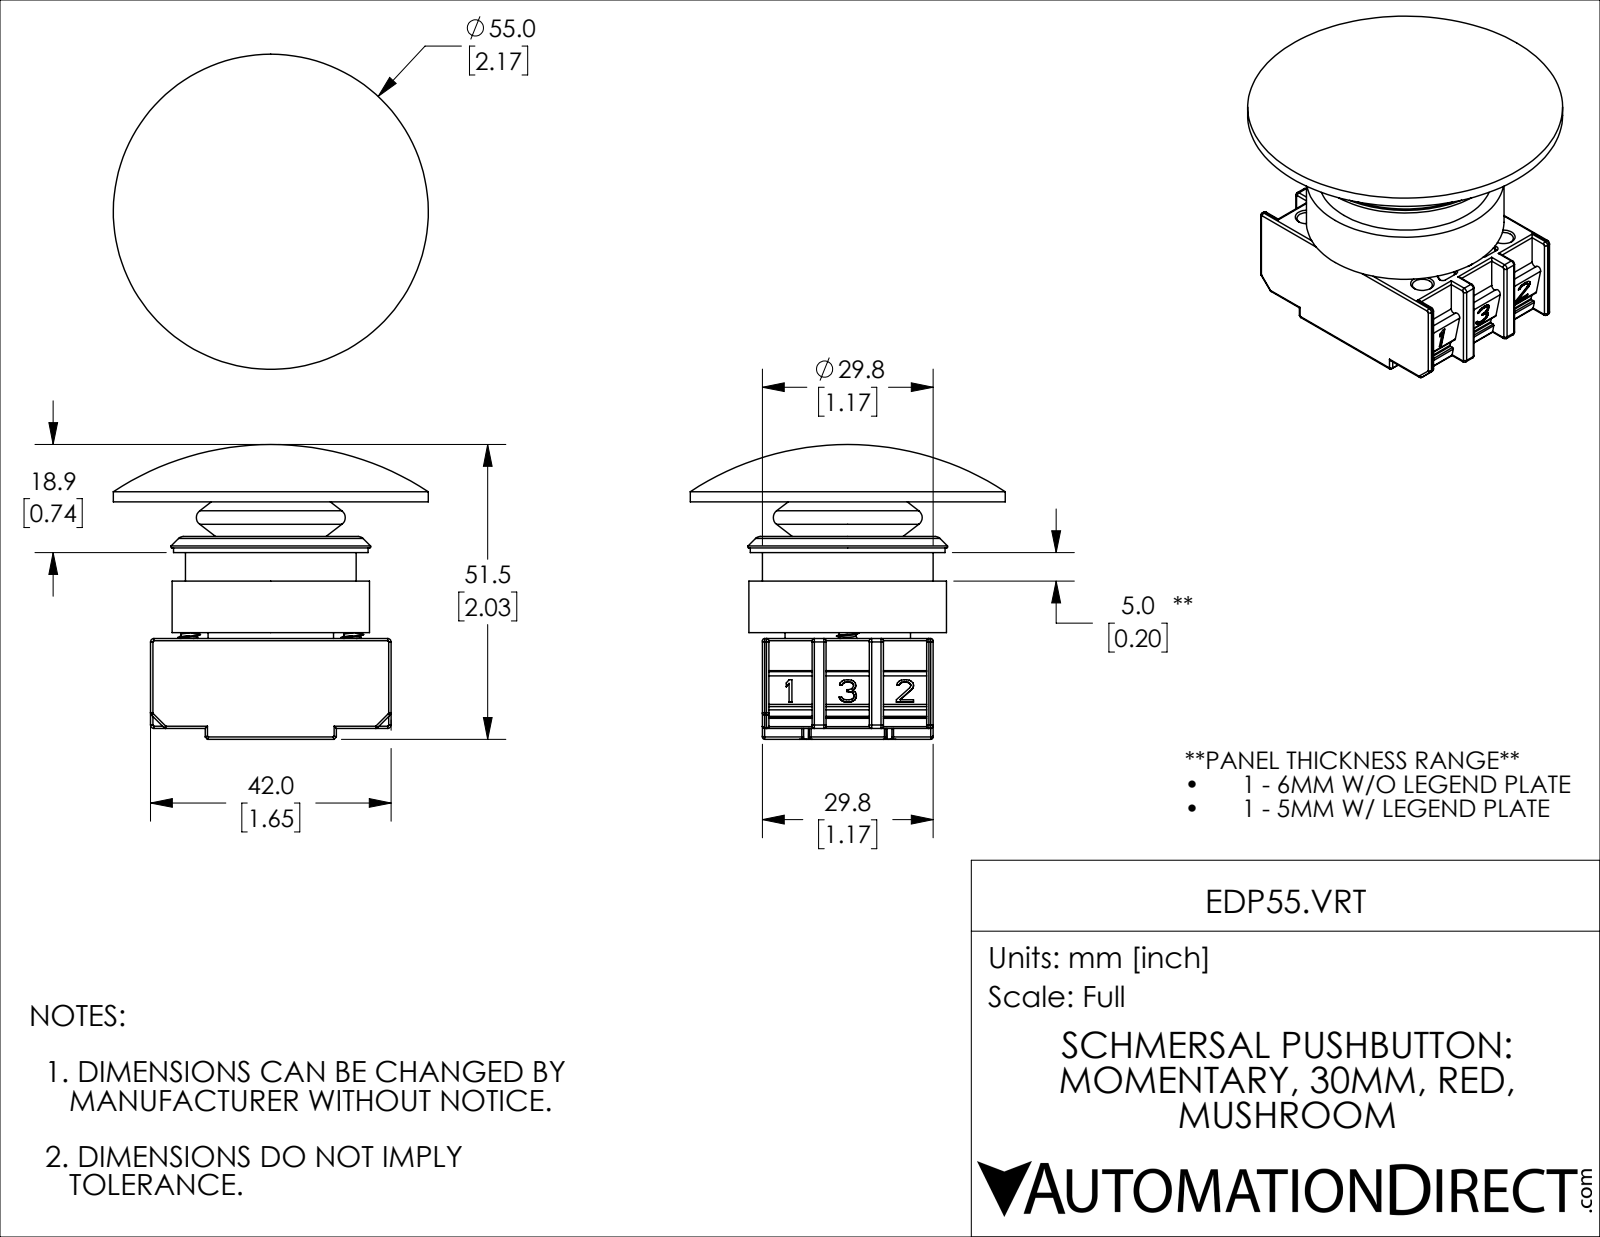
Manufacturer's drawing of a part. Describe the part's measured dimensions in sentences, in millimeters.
The part is named "EDP55.VRT". Its 3-D file was written by "SolidWorks 2019 (CONFIG_CONTROL_DESIGN)". It is 5 solids with 1491 faces: 538 planar, 502 cylindrical and 451 other. Overall it measures 55 by 55 by 51.45 millimeters. Its volume is 39 129 cubic millimeters and its surface area 26 353 square millimeters. Round holes: 6 of diameter 3.5, 6 of diameter 5.15, 1 of diameter 12.15, 1 of diameter 17, 1 of diameter 18.8, 1 of diameter 19.5, 1 of diameter 24.1, 1 of diameter 24.2, 1 of diameter 26, 1 of diameter 30.2, 1 of diameter 32. Round bosses or shafts: 2 of diameter 4.8, 2 of diameter 2.93, 1 of diameter 55, 1 of diameter 34.5, 1 of diameter 34, 1 of diameter 29.8, 1 of diameter 25.5, 1 of diameter 24. Partial cylindrical surfaces (rounded edges, fillets, slot ends): 112 of radius 0.4, 48 of radius 0.3, 28 of radius 0.2, 8 of radius 0.6, 6 of radius 0.5, 6 of radius 0.8, 2 of radius 0.1, 2 of radius 0.6. The main face-to-face distances are 18.6, 29.8, 1, 41.45, 17.6, 22.85, 1.9, 16.8, 23.85, 35.4. The hole center spacings are 10, 17.41, 30.2, 28.5, 14.25, 20, 34.82.
